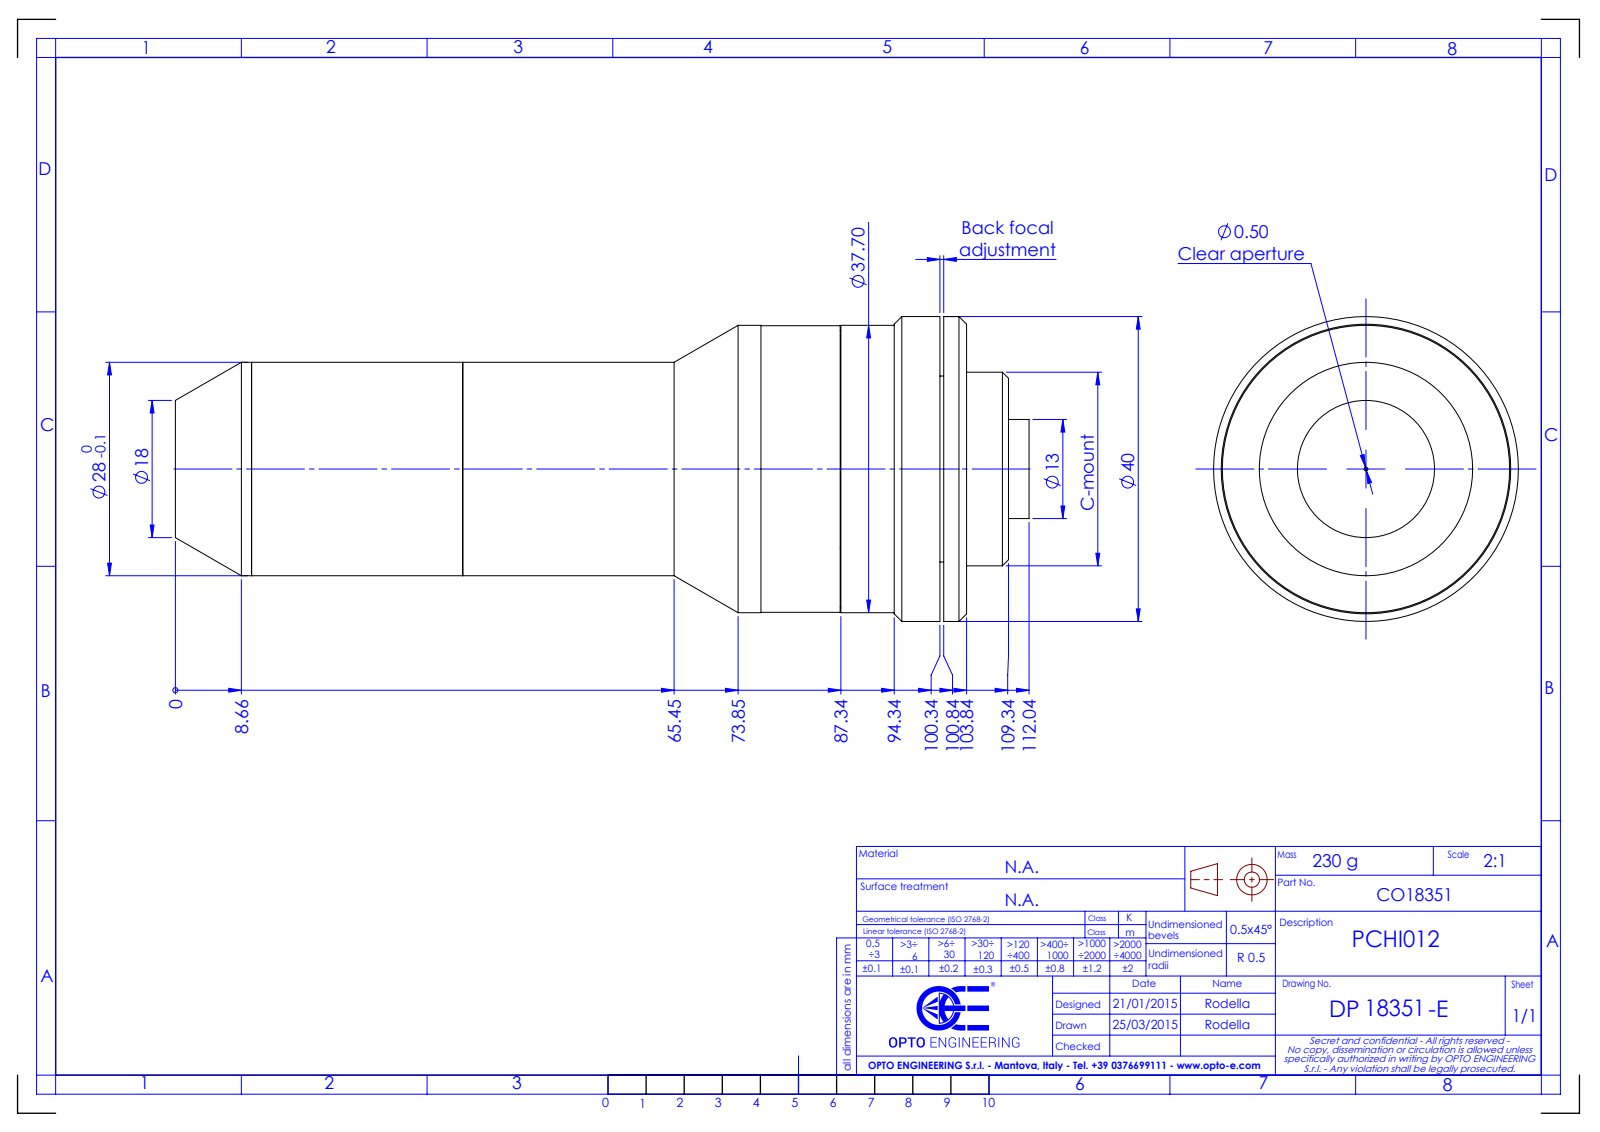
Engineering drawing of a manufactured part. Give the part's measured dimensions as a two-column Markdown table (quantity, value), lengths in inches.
| quantity | value |
| --- | --- |
| part name | DP18351-E_PCHI012 |
| STEP written by | SolidWorks 2021 (CONFIG_CONTROL_DESIGN) |
| units | inches |
| bodies | 0 solids, 55 faces (15 planar, 26 cylindrical, 14 other) |
| overall size | 4.411 × 1.575 × 1.575 |
| round holes (diameter × count) | 0.256 × 1, 0.886 × 1 |
| round bosses / shafts (diameter × count) | 1.575 × 1, 1.484 × 1, 1.48 × 1, 1.102 × 1, 1 × 1, 0.866 × 1, 0.512 × 1 |
| main face-to-face distances | 0.02, 0.138, 0.118, 0.512, 0.531, 0.65, 3.045, 3.557, 3.576, 3.694 |
